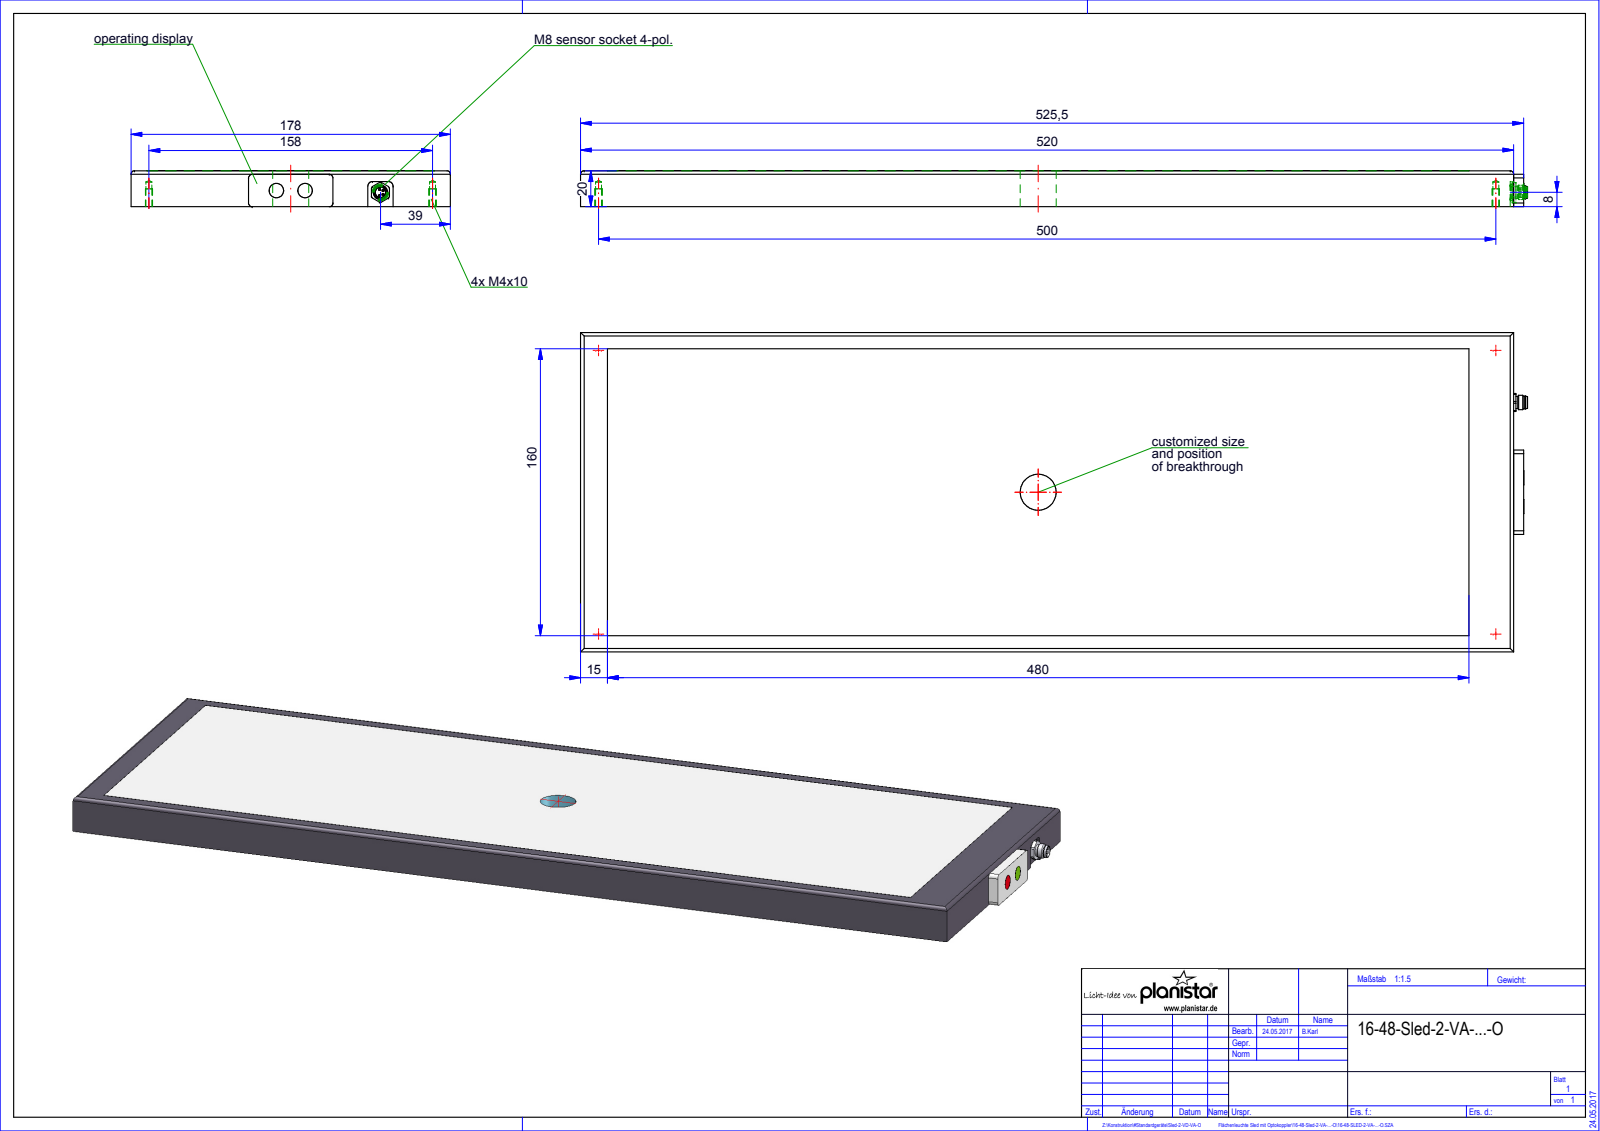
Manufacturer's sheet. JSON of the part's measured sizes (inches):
{"part_name": "Root; Baugruppe_Xled-2-VD; QUADER_0; 09-3391-00-04", "step_written_by": "HiCAD 2015 2002.1 Build 408 (AUTOMOTIVE_DESIGN)", "units": "inches", "bodies": {"solids": 3, "faces": 90, "planar": 39, "cylindrical": 38, "other": 13}, "overall_size": [20.776, 7.008, 0.791], "volume_in3": 113.2, "surface_area_in2": 335.3, "round_holes": [[0.13, 4], [0.157, 4], [0.228, 1], [0.787, 1]], "round_bosses_or_shafts": [[0.039, 4], [0.315, 3], [0.283, 1], [0.268, 1], [0.252, 1]], "partial_cylinders_radius": [[0.079, 8], [0.098, 2], [0.217, 1]], "face_to_face_distances": [0.791, 0.787, 7.008, 20.472, 20.689, 0.217, 0.079, 0.083, 0.709, 20.394], "hole_center_spacings": [6.22, 10.135, 10.51, 19.685, 20.644]}
